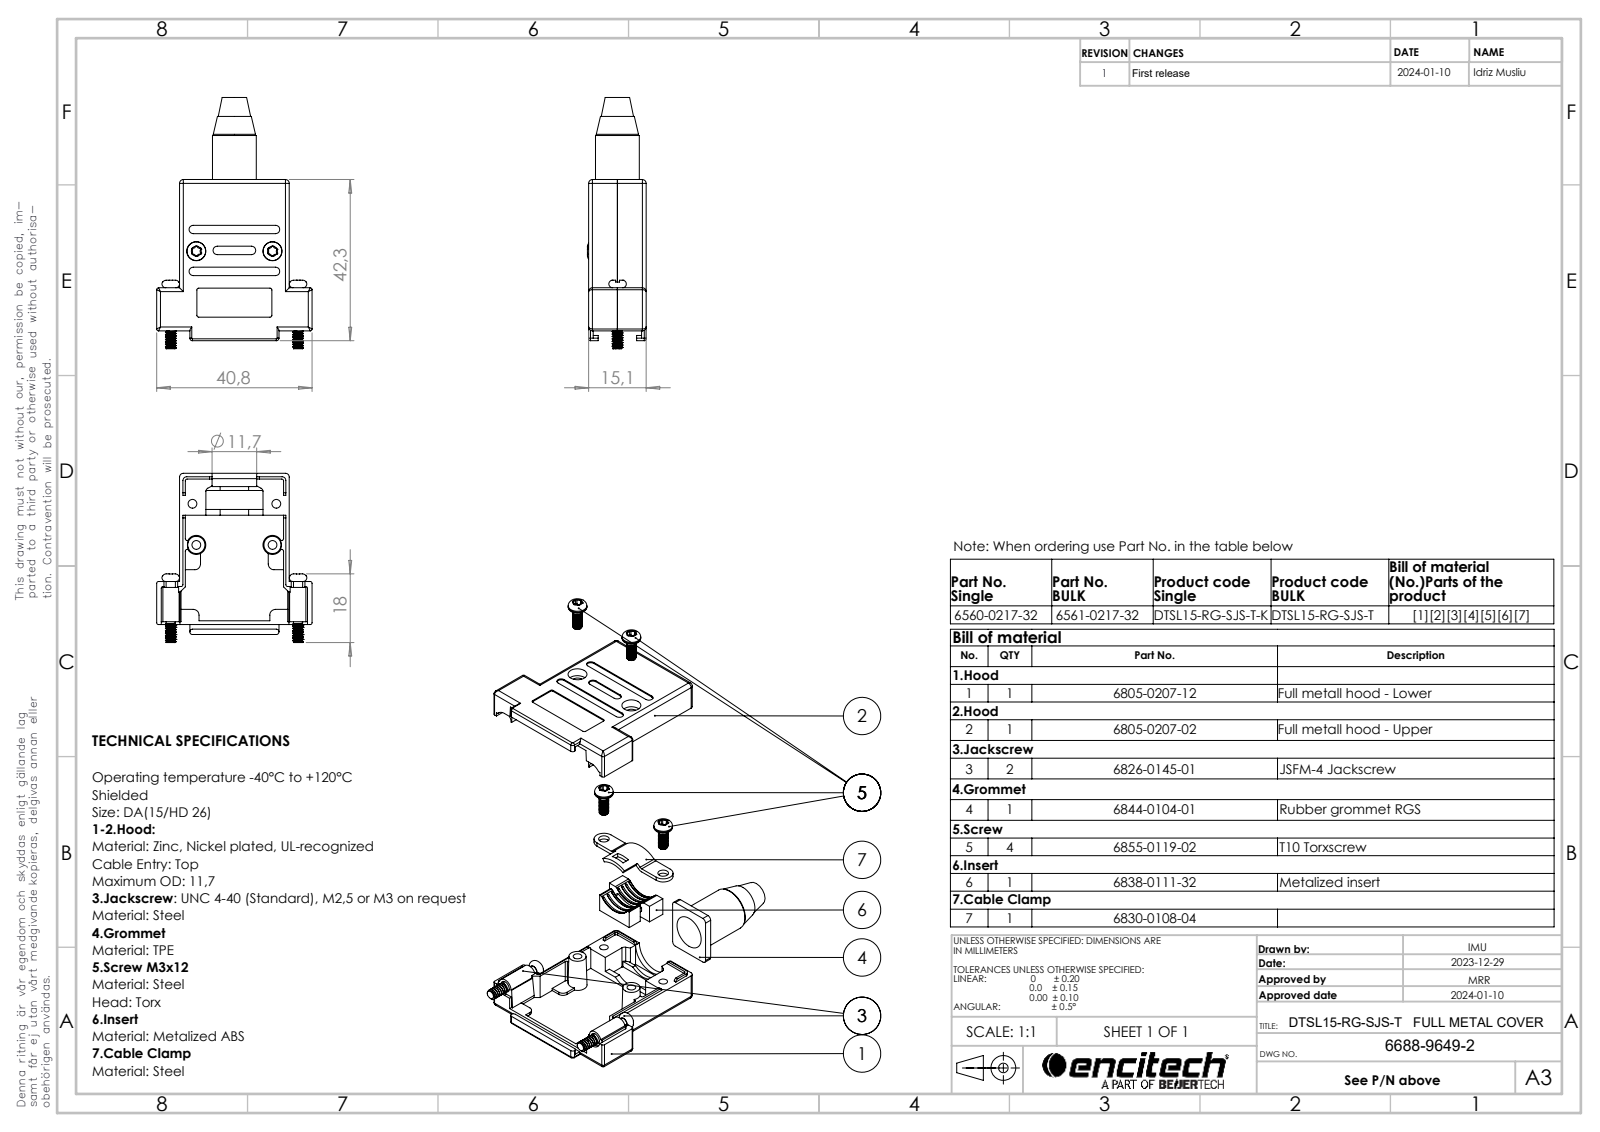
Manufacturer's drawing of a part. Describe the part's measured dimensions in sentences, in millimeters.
The part is named "6560-0217-32; 6805-0207-02; 6830-0108-04; 6855-0119-01 (+4 more)". Its 3-D file was written by "SolidWorks 2021 (AUTOMOTIVE_DESIGN)". It is 15 solids with 987 faces: 389 planar, 504 cylindrical and 94 other. Overall it measures 65.95 by 40.8 by 15.4 millimeters. Its volume is 9 231 cubic millimeters and its surface area 13 891 square millimeters. Round holes: 4 of diameter 2.3, 4 of diameter 2.8, 2 of diameter 3.1, 2 of diameter 5, 1 of diameter 9, 1 of diameter 11.7. Round bosses or shafts: 4 of diameter 4.9, 4 of diameter 2.5, 2 of diameter 2.8, 2 of diameter 2.4, 1 of diameter 11.5, 1 of diameter 11.1. Partial cylindrical surfaces (rounded edges, fillets, slot ends): 30 of radius 0.5, 30 of radius 0.7, 26 of radius 1, 24 of radius 0.18, 8 of radius 1.1, 4 of radius 1.5, 4 of radius 1.8, 4 of radius 3.62. The main face-to-face distances are 1.35, 13.75, 15.1, 12.4, 7.55, 6.2, 1.05, 1.5, 14.8, 7.25. The hole center spacings are 10.85, 16.71, 23.61, 20, 22, 33.42.
